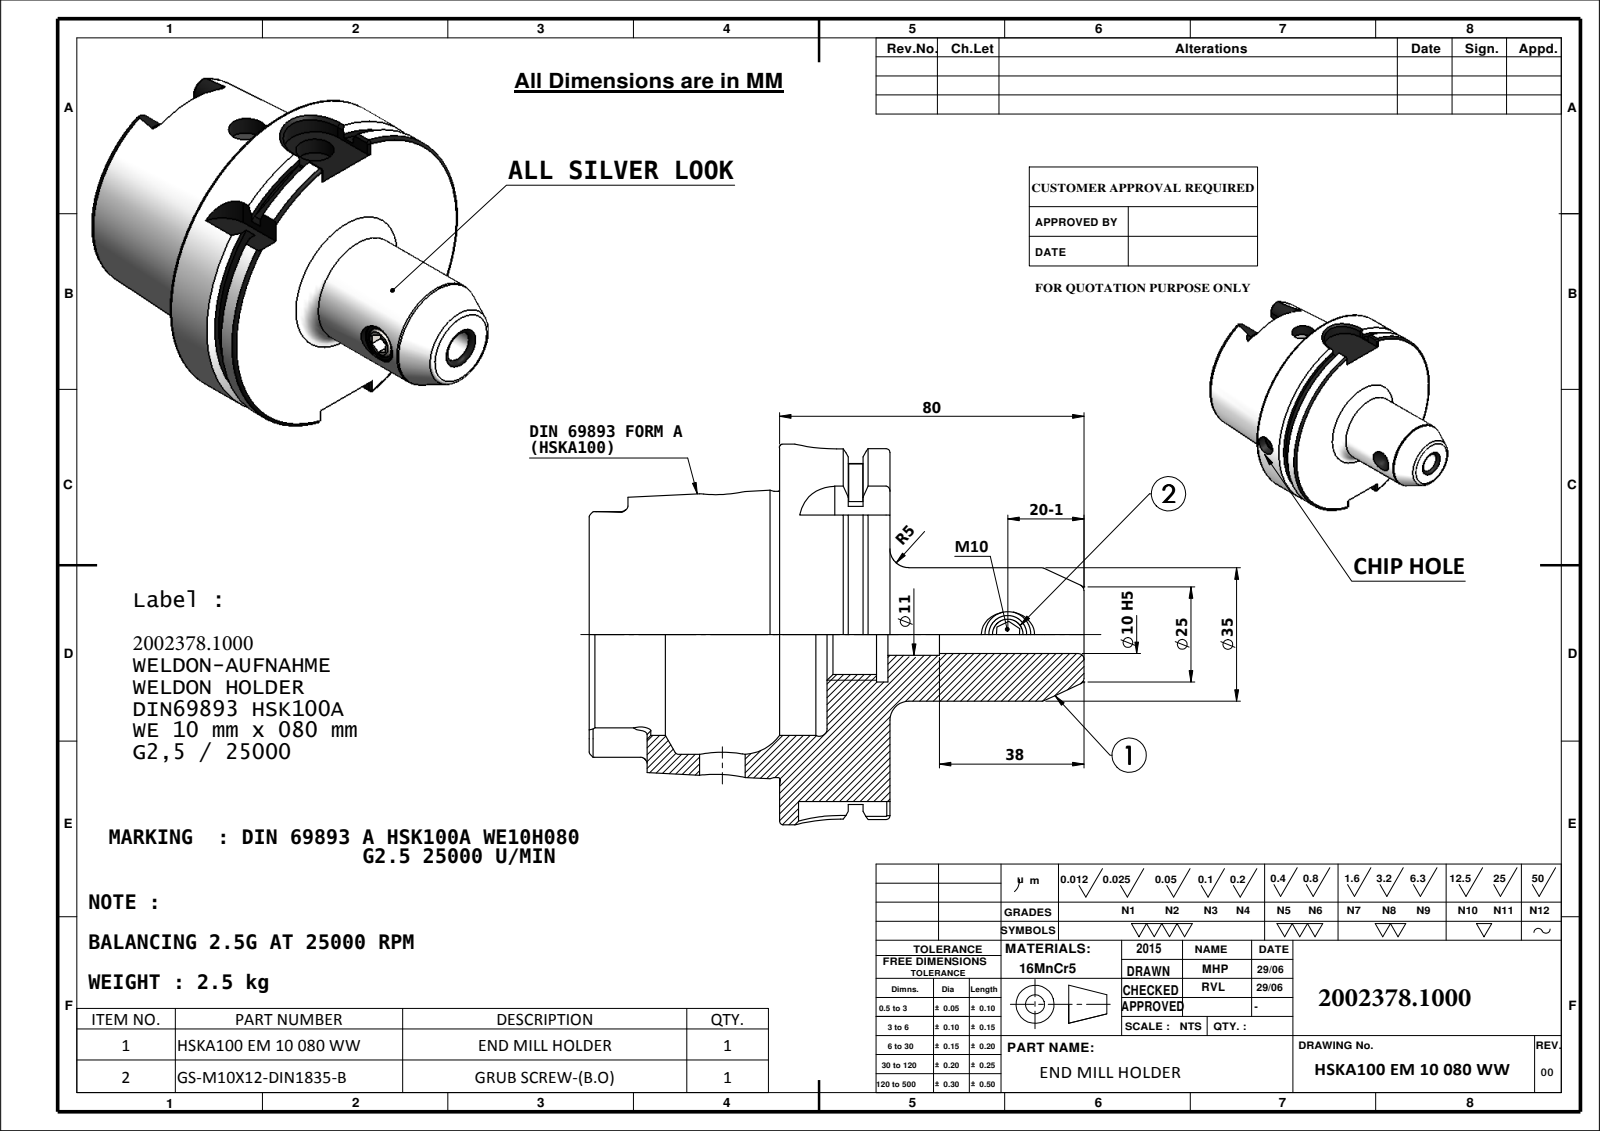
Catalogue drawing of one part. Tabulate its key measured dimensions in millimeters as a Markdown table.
| quantity | value |
| --- | --- |
| part name | 91100A-WE8 10080; HSKA100 EM 10 080 WW; M10X12 |
| STEP written by | SolidWorks 2009 (CONFIG_CONTROL_DESIGN) |
| units | millimeters |
| bodies | 2 solids, 201 faces (63 planar, 56 cylindrical, 82 other) |
| overall size | 130 × 100 × 100 |
| volume | 296 448 mm³ |
| surface area | 57 087 mm² |
| round holes (diameter × count) | 12 × 3, 10 × 2, 8.5 × 1, 11 × 1, 21 × 1, 25 × 1, 53 × 1, 63 × 1 |
| round bosses / shafts (diameter × count) | 100 × 1, 92 × 1, 75.16 × 1, 35 × 1, 10 × 1 |
| partial cylindrical surfaces (radius × count) | 1.8 × 6, 4.88 × 4, 10 × 2, 11 × 1 |
| main face-to-face distances | 29, 16.5, 12.5, 50, 62.5, 79, 71.93, 21.93, 9.43, 7.07 |
| hole center spacings | 30, 53 |
